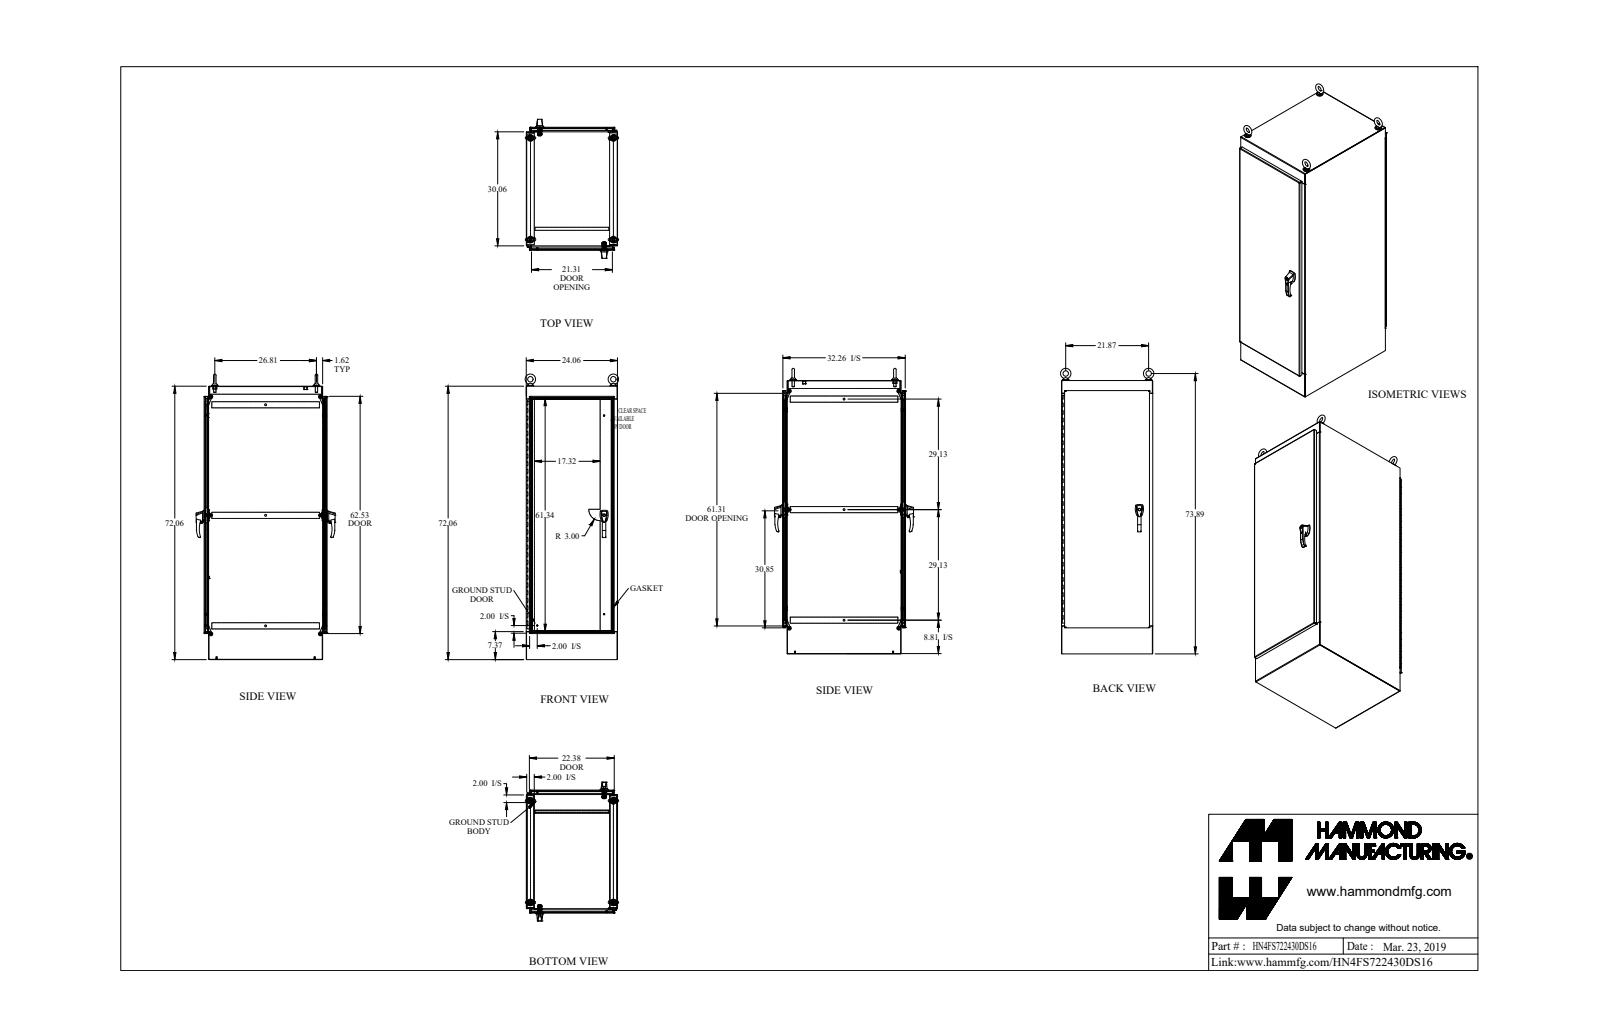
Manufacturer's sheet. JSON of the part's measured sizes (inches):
{"part_name": "HN4FS722430DS16", "step_written_by": "SolidWorks 2018 (AUTOMOTIVE_DESIGN)", "units": "inches", "bodies": {"solids": 95, "faces": 3325, "planar": 1460, "cylindrical": 1537, "other": 328}, "overall_size": [75.256, 36.664, 24.604], "volume_in3": 1172, "surface_area_in2": 24543, "round_holes": [[0.304, 20], [0.35, 8], [0.25, 4], [0.257, 4], [0.28, 4], [0.281, 4], [0.313, 4], [0.39, 4], [0.413, 4], [0.625, 4], [0.68, 4], [0.75, 4]], "round_bosses_or_shafts": [[1.75, 4], [1.5, 4], [1.25, 4], [1, 4], [0.75, 4], [0.738, 4], [0.63, 4], [0.625, 4]], "partial_cylinders_radius": [[0.125, 44], [0.043, 42], [0.138, 36], [0.017, 32], [0.048, 26], [0.143, 26], [0.5, 26], [0.06, 21]], "face_to_face_distances": [0.095, 23.965, 32.339, 23.87, 24.06, 1.187, 31.152, 32.244, 71.965, 32.434], "hole_center_spacings": [6, 23.099, 12, 25.329, 18, 28.663, 24, 32.765]}
